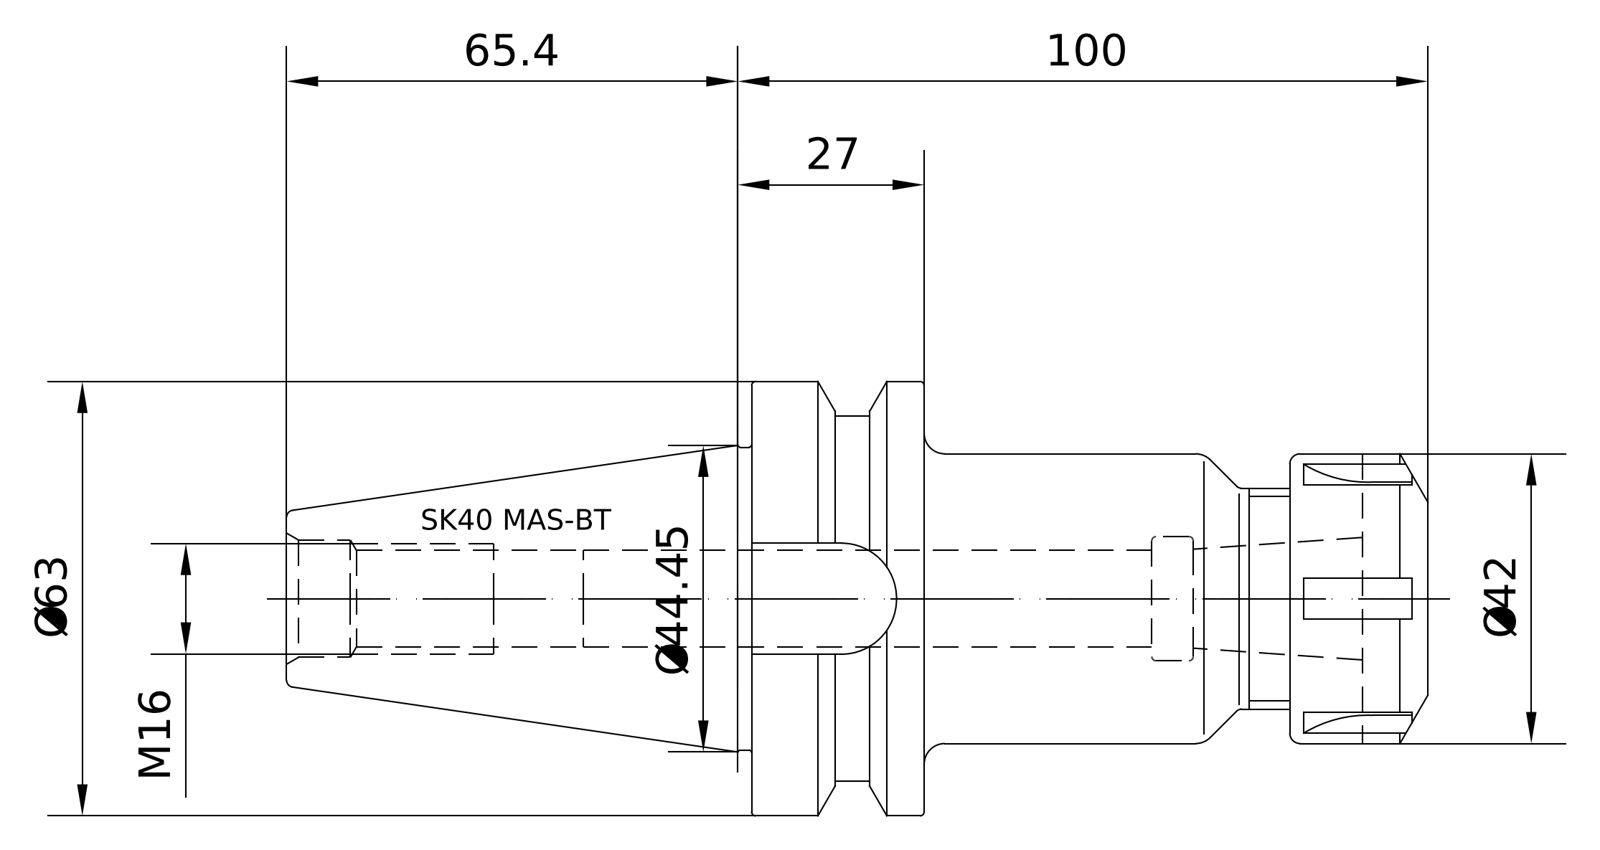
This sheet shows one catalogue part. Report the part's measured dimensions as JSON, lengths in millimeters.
{"part_name": "40-521-25; 83-912-25; 40-521-25_ASM", "step_written_by": "PRO/ENGINEER BY PARAMETRIC TECHNOLOGY CORPORATION, 2010430 (CONFIG_CONTROL_DESIGN)", "units": "millimeters", "bodies": {"solids": 2, "faces": 146, "planar": 46, "cylindrical": 26, "other": 74}, "overall_size": [165.4, 62.98, 62.98], "volume_mm3": 211800, "surface_area_mm2": 36540, "round_holes": [[13.84, 1], [17.01, 1], [17.5, 1], [18, 1]], "round_bosses_or_shafts": [[62.98, 1], [52.75, 1], [43.75, 1], [42, 1], [32, 1], [16.01, 1]], "partial_cylinders_radius": [[8.1, 1]], "face_to_face_distances": [53, 25, 78, 98, 73, 20, 44.9, 86, 61, 8]}
